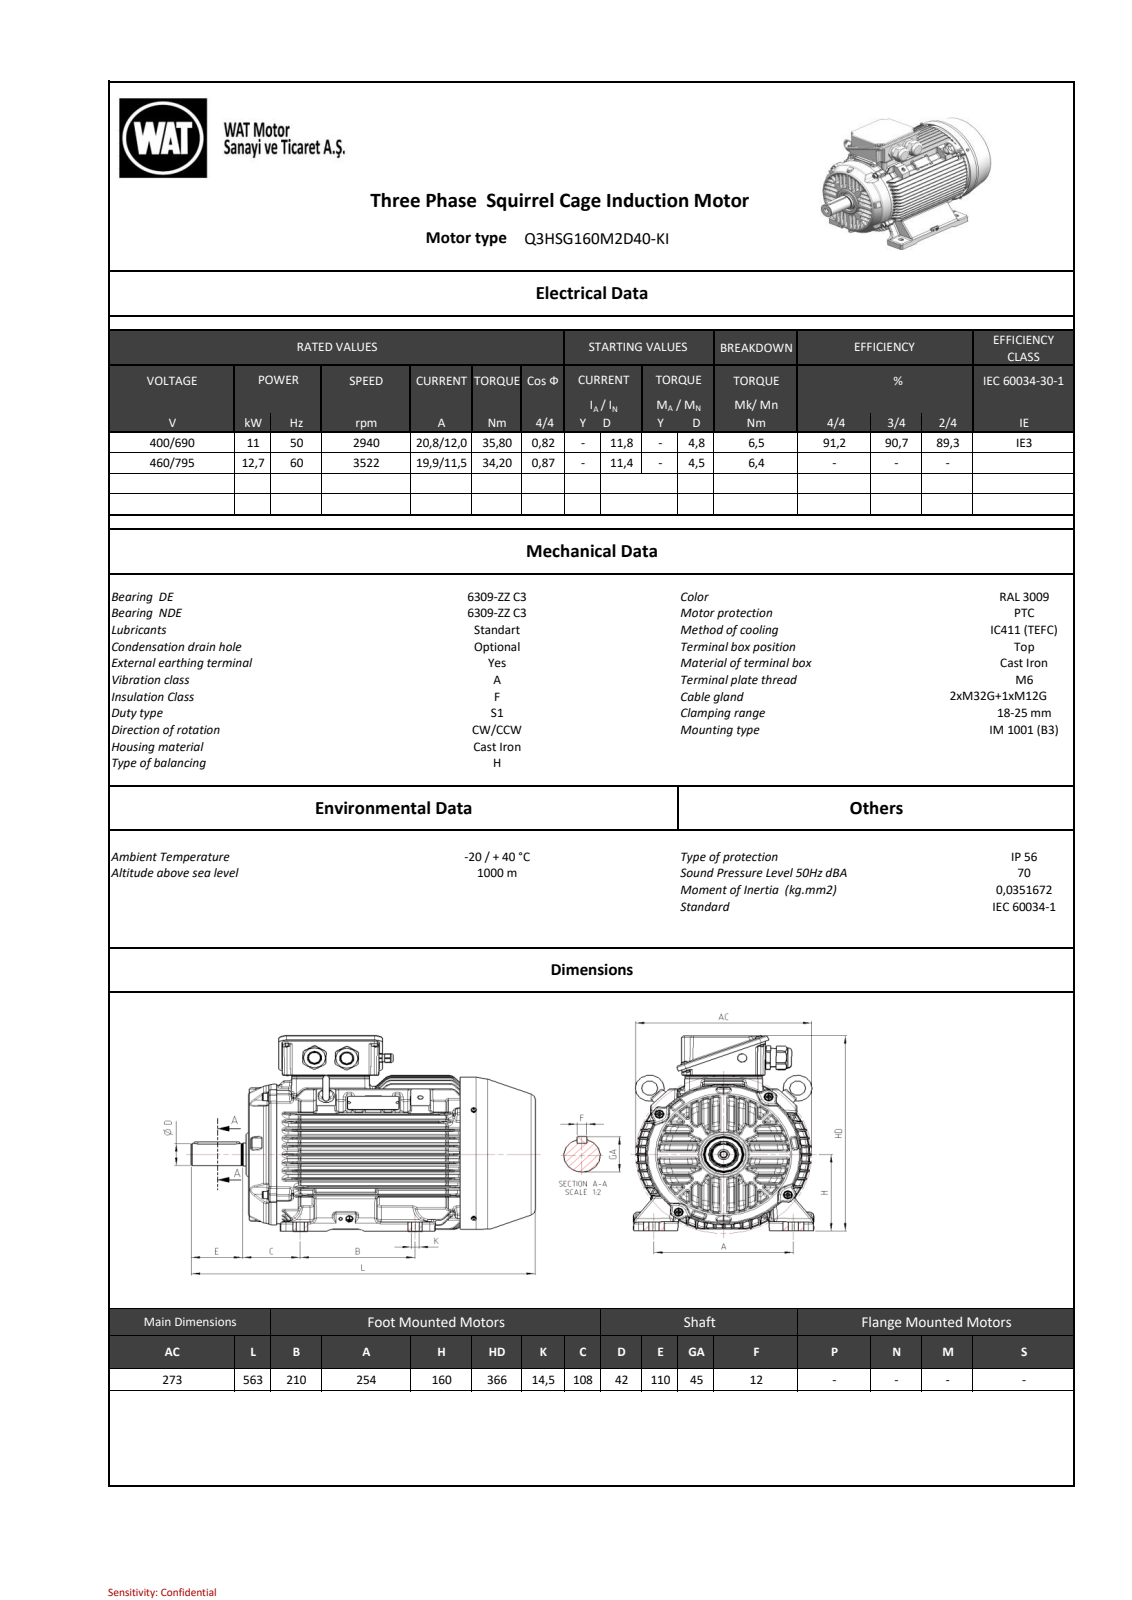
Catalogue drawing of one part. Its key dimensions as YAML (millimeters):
part_name: "C9017F38B806sw1s"
step_written_by: "SIEMENS PLM Software NX 11.0 (AUTOMOTIVE_DESIGN)"
units: millimeters
bodies: {solids: 0, faces: 7014, planar: 1351, cylindrical: 1896, other: 3767}
overall_size: [563, 365.99, 317.6]
round_holes:
  - {diameter: 6.8, count: 8}
  - {diameter: 2.5, count: 2}
  - {diameter: 8.5, count: 2}
  - {diameter: 19, count: 2}
  - {diameter: 21, count: 2}
  - {diameter: 4.2, count: 1}
  - {diameter: 6, count: 1}
  - {diameter: 10.2, count: 1}
  - {diameter: 11.3, count: 1}
  - {diameter: 13, count: 1}
  - {diameter: 24.5, count: 1}
  - {diameter: 68.67, count: 1}
round_bosses_or_shafts:
  - {diameter: 16, count: 4}
  - {diameter: 13, count: 4}
  - {diameter: 10, count: 4}
  - {diameter: 8.65, count: 4}
  - {diameter: 8, count: 4}
  - {diameter: 5, count: 4}
  - {diameter: 36, count: 2}
  - {diameter: 34.5, count: 2}
partial_cylinders:
  - {radius: 3, count: 233}
  - {radius: 4.5, count: 212}
  - {radius: 1.5, count: 106}
  - {radius: 2, count: 76}
  - {radius: 4, count: 72}
  - {radius: 1.8, count: 64}
  - {radius: 6, count: 57}
  - {radius: 0.4, count: 39}
face_to_face_distances: [13.76, 13.83, 27.59, 27.73, 13.9, 41.49, 55.44, 41.68, 27.85, 13.95]
hole_center_spacings: [121.5, 171.83, 42.2, 139.38, 199.06, 239.31, 243.01, 35.5]
